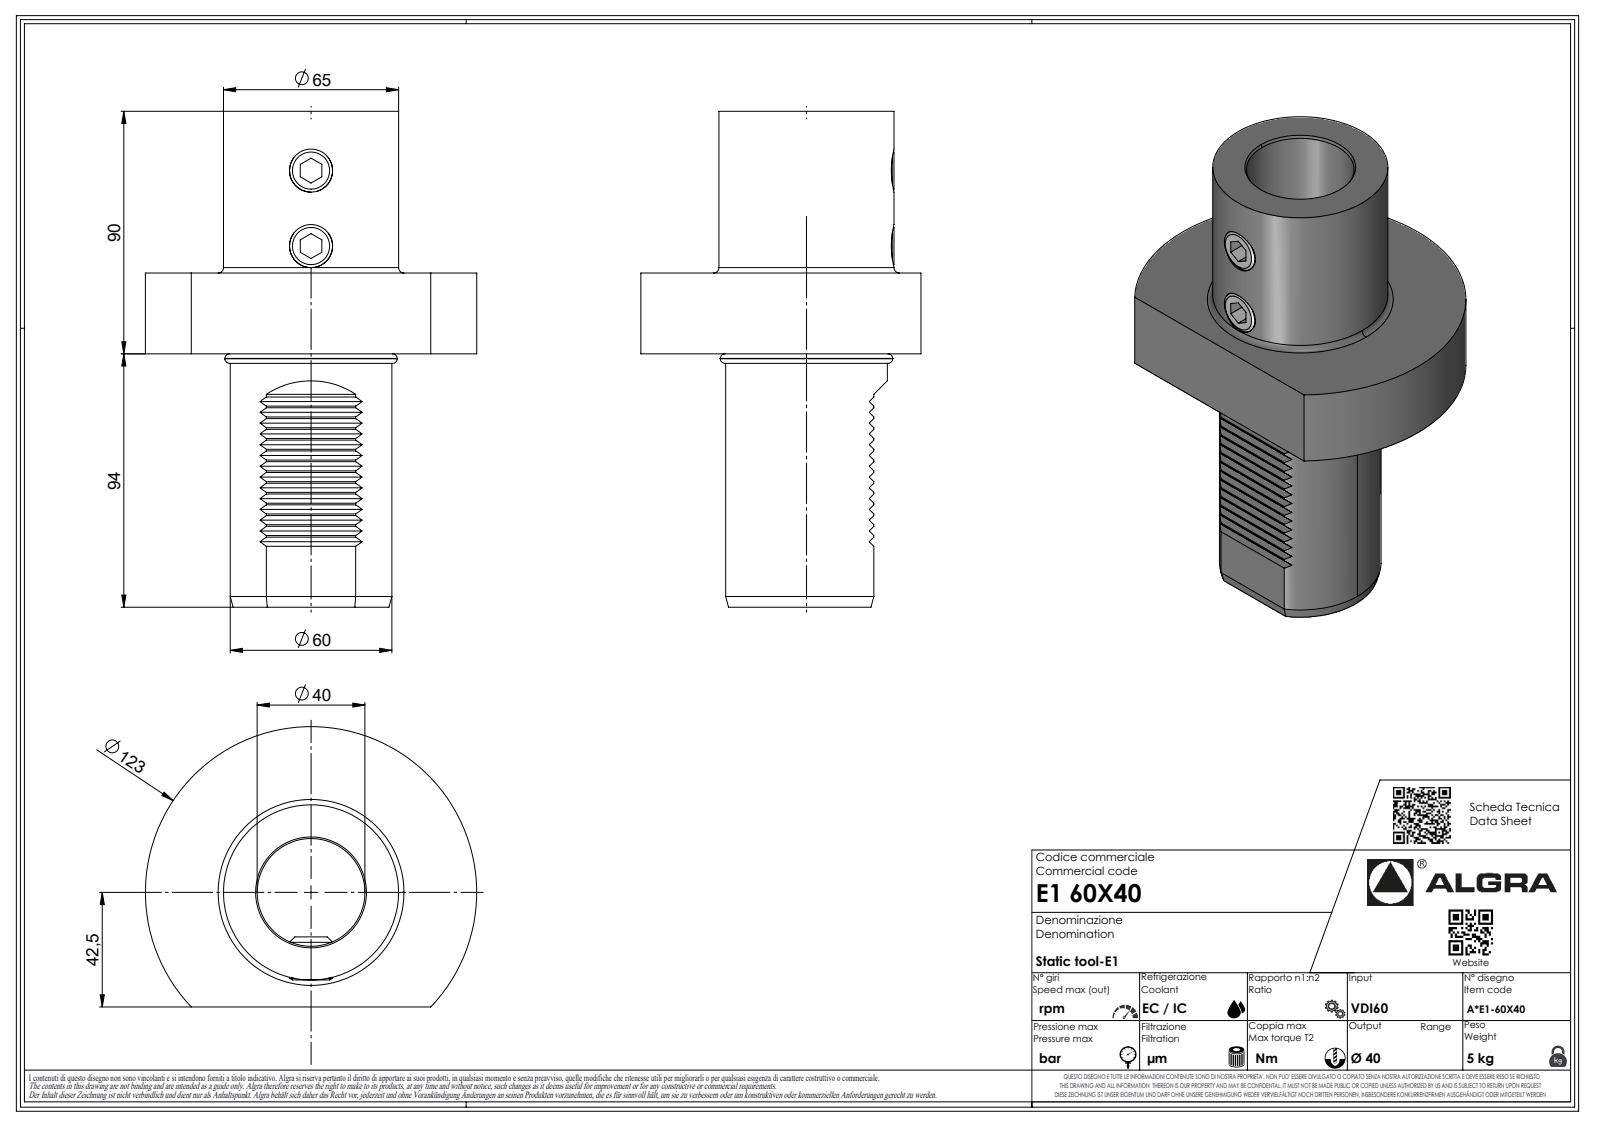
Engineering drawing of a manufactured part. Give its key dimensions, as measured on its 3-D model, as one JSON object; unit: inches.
{"part_name": "E160X40", "step_written_by": "SolidWorks 2023 (AUTOMOTIVE_DESIGN)", "units": "inches", "bodies": {"solids": 1, "faces": 296, "planar": 202, "cylindrical": 49, "other": 45}, "overall_size": [7.244, 4.843, 4.094], "volume_in3": 41.87, "surface_area_in2": 112.8, "round_holes": [[0.63, 2], [0.083, 1], [1.575, 1]], "round_bosses_or_shafts": [[2.559, 1], [2.527, 1], [2.362, 1], [0.251, 1], [0.067, 1]], "partial_cylinders_radius": [[0.013, 7], [0.02, 7], [0.146, 7], [0.008, 1], [2.421, 1]], "face_to_face_distances": [1.181, 4.882, 3.701, 2.362, 3.543, 7.244, 0.111, 0.557, 0.445, 0.669], "hole_center_spacings": [0.849, 1.102, 1.917]}
